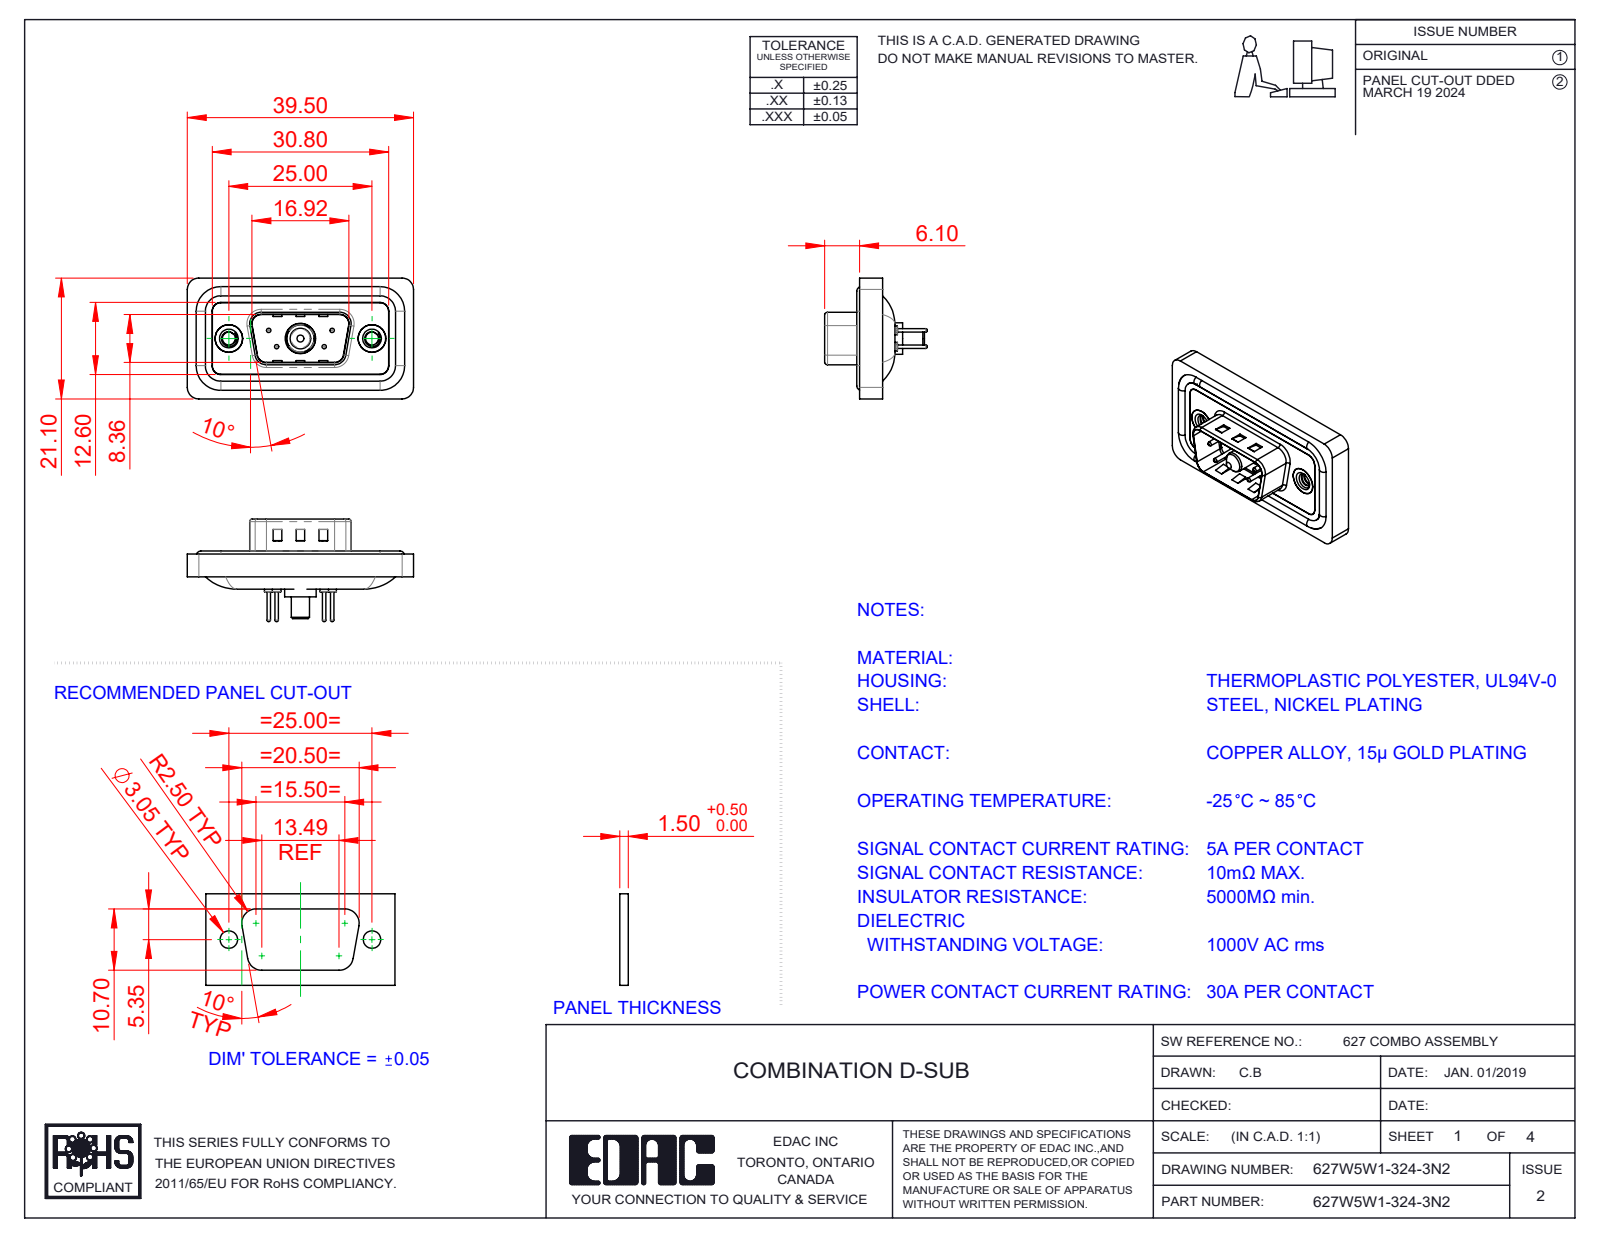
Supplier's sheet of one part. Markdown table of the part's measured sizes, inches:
| quantity | value |
| --- | --- |
| part name | 627Combo Housing_5W1; 627Combo Contact Row 2_24; 627Combo Threaded Rivet_2; 627Combo Waterproof Housing_09 Contacts (+5 more) |
| STEP written by | SolidWorks 2023 (CONFIG_CONTROL_DESIGN) |
| units | inches |
| bodies | 13 solids, 598 faces (183 planar, 255 cylindrical, 160 other) |
| overall size | 1.555 × 0.831 × 0.705 |
| volume | 0.268 in³ |
| surface area | 10.77 in² |
| round holes (diameter × count) | 0.03 × 4, 0.063 × 4, 0.079 × 4, 0.089 × 2, 0.157 × 2, 0.189 × 2, 0.197 × 2, 0.191 × 1, 0.209 × 1 |
| round bosses / shafts (diameter × count) | 0.063 × 4, 0.059 × 4, 0.024 × 4, 0.193 × 2, 0.217 × 1, 0.205 × 1, 0.187 × 1, 0.148 × 1 |
| partial cylindrical surfaces (radius × count) | 0.059 × 22, 0.079 × 18, 0.02 × 8, 0.063 × 8, 0.01 × 4, 0.024 × 4, 0.026 × 4, 0.035 × 4 |
| main face-to-face distances | 0.016, 0.043, 0.114, 0.063, 0.122, 0.059, 0.02, 0.098, 0.157, 0.031 |
| hole center spacings | 0.124, 0.225, 0.28, 0.492, 0.713, 0.173, 0.173, 0.327 |
